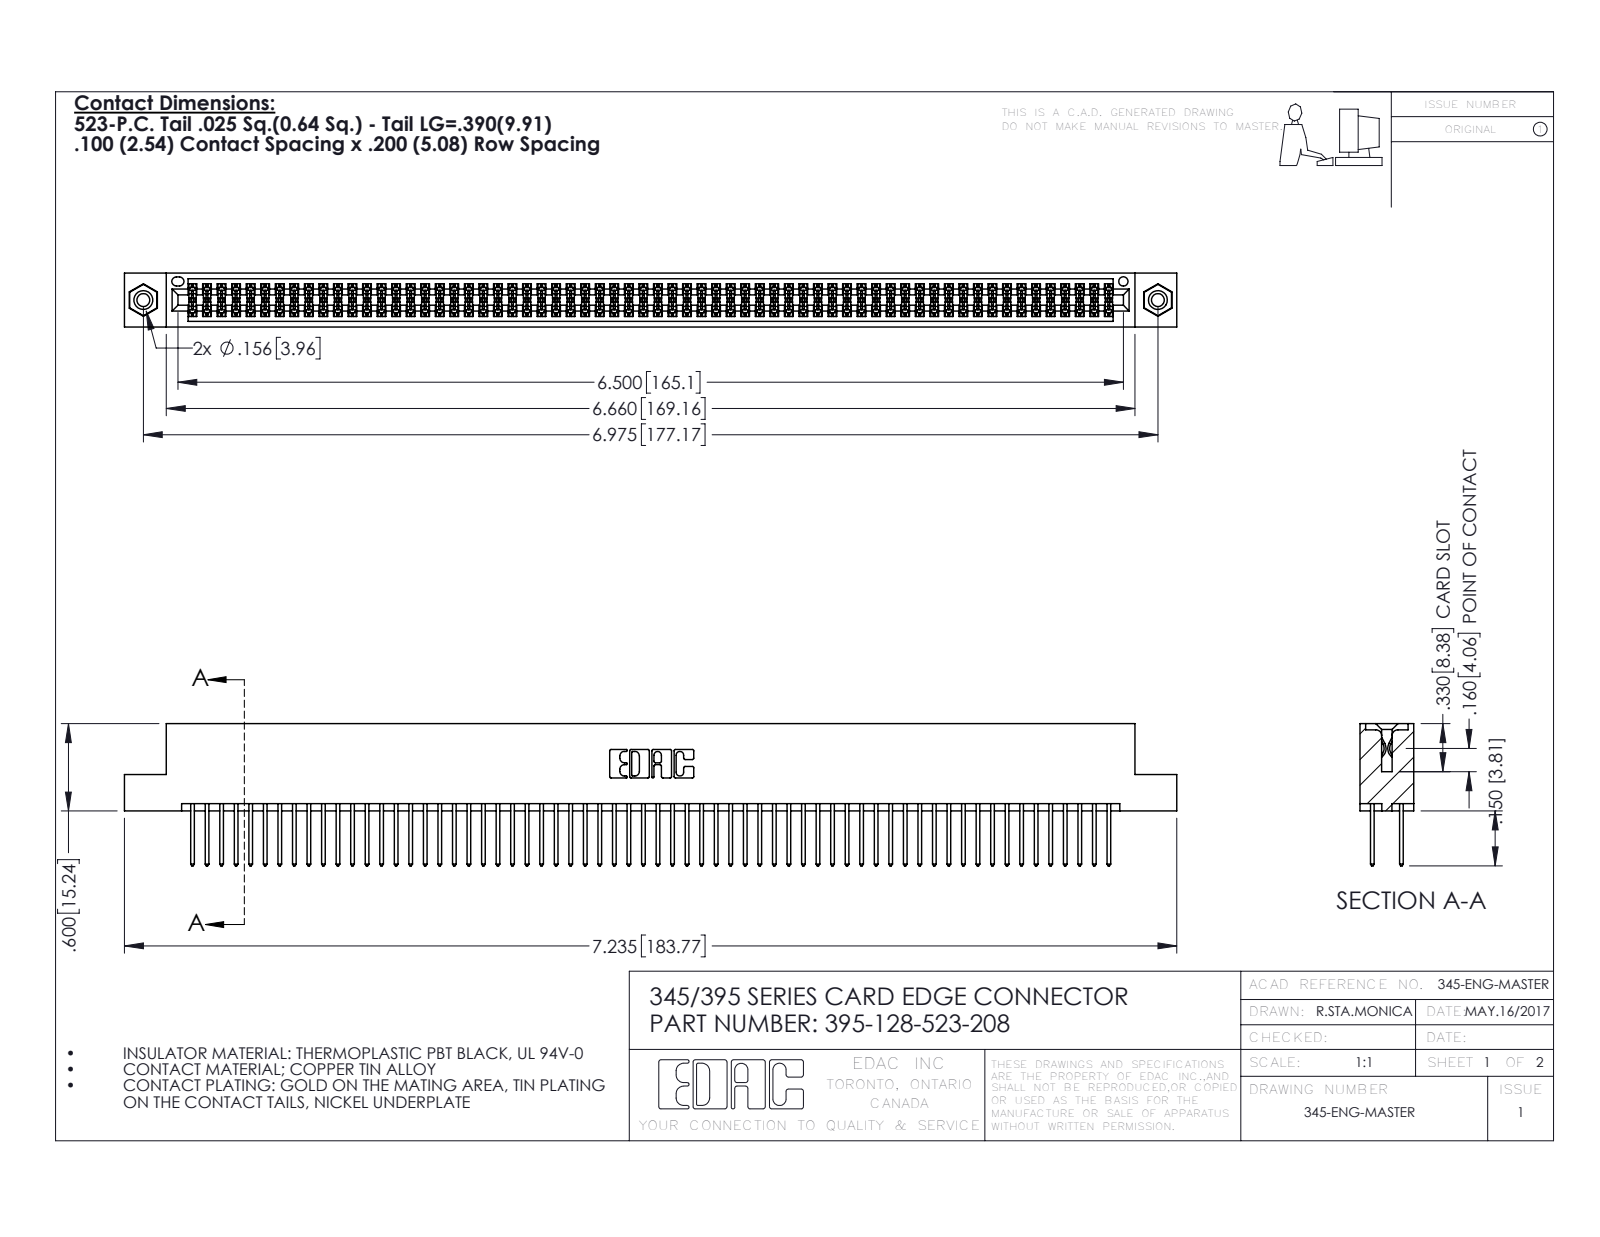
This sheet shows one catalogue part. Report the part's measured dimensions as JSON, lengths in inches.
{"part_name": "345-250-001_345-250-003-102; 345-292-001_345-293-123; 395-128-523-208; 345 Part_Flush Mounting Lugs - 0.156 Dia-TI", "step_written_by": "SolidWorks 2016 (CONFIG_CONTROL_DESIGN)", "units": "inches", "bodies": {"solids": 131, "faces": 6586, "planar": 4336, "cylindrical": 2234, "other": 16}, "overall_size": [7.235, 0.977, 0.37], "volume_in3": 1.117, "surface_area_in2": 44.46, "round_holes": [[0.089, 2], [0.125, 2], [0.156, 2], [0.064, 1]], "round_bosses_or_shafts": [[0.155, 2]], "partial_cylinders_radius": [[0.006, 192], [0.01, 128], [0.01, 22], [0.007, 6], [0.031, 6], [0.026, 3], [0.014, 2], [0.019, 2]], "face_to_face_distances": [0.072, 0.298, 0.2, 0.098, 0.272, 0.025, 0.37, 0.225, 0.175, 0.149], "hole_center_spacings": [0.27, 6.739, 6.975]}
